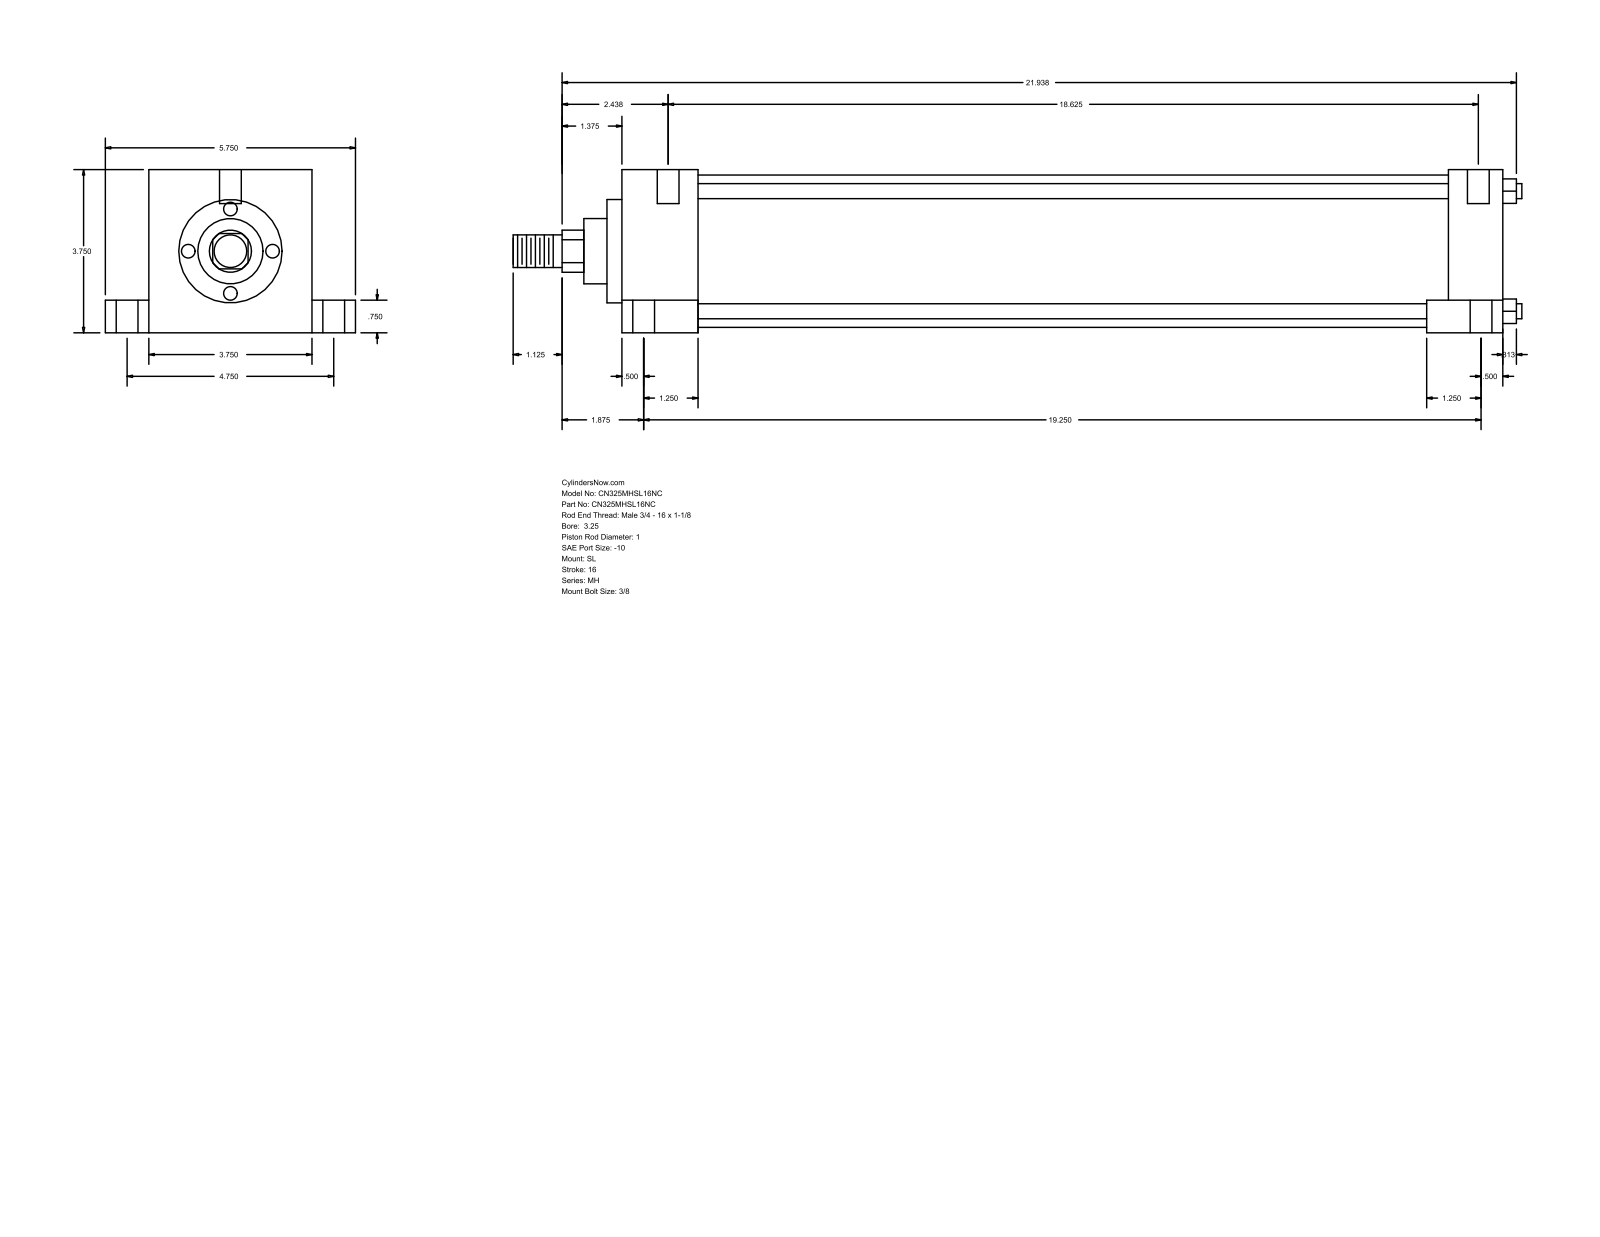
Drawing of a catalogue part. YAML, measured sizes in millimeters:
part_name: "MH_SL__0325_1"
step_written_by: "GSSL Pune (CONFIG_CONTROL_DESIGN)"
units: millimeters
bodies: {solids: 0, faces: 110, planar: 77, cylindrical: 33, other: 0}
overall_size: [588.96, 146.05, 95.25]
round_holes:
  - {diameter: 12.7, count: 6}
  - {diameter: 5.56, count: 4}
  - {diameter: 19.05, count: 4}
round_bosses_or_shafts:
  - {diameter: 8.76, count: 4}
  - {diameter: 88.9, count: 1}
  - {diameter: 60.33, count: 1}
  - {diameter: 38.1, count: 1}
  - {diameter: 25.4, count: 1}
  - {diameter: 19.05, count: 1}
partial_cylinders:
  - {radius: 12.29, count: 1}
face_to_face_distances: [95.24, 514.35, 44.46, 469.89, 25.41, 120.65, 19.05, 76.19, 482.6, 438.14]
hole_center_spacings: [60.35, 60.41, 61.65, 62, 120.66, 478.49, 479.42, 480.06]
